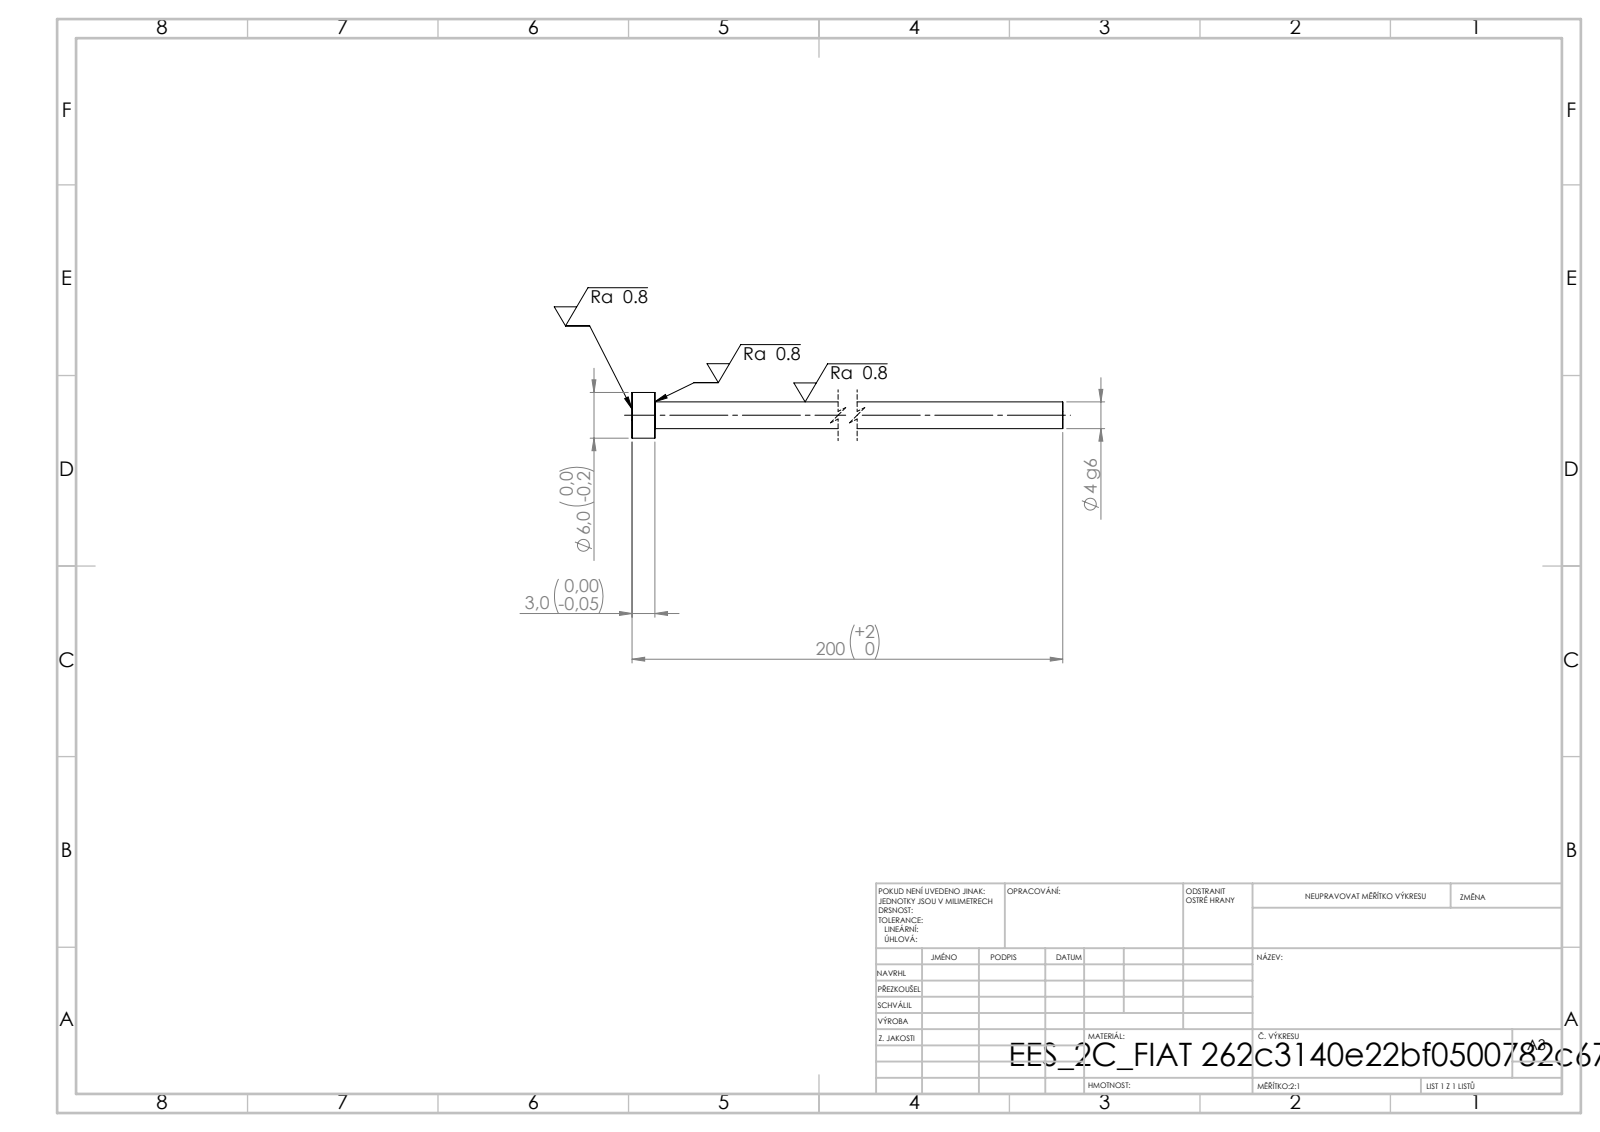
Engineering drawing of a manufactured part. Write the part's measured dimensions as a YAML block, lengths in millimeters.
step_written_by: "SolidWorks 2019 (CONFIG_CONTROL_DESIGN)"
units: millimeters
bodies: {solids: 1, faces: 7, planar: 3, cylindrical: 4, other: 0}
overall_size: [200, 6, 6]
volume: 1980
surface_area: 2279
round_bosses_or_shafts:
  - {diameter: 6, count: 1}
  - {diameter: 3.5, count: 1}
face_to_face_distances: [3, 200, 197]
